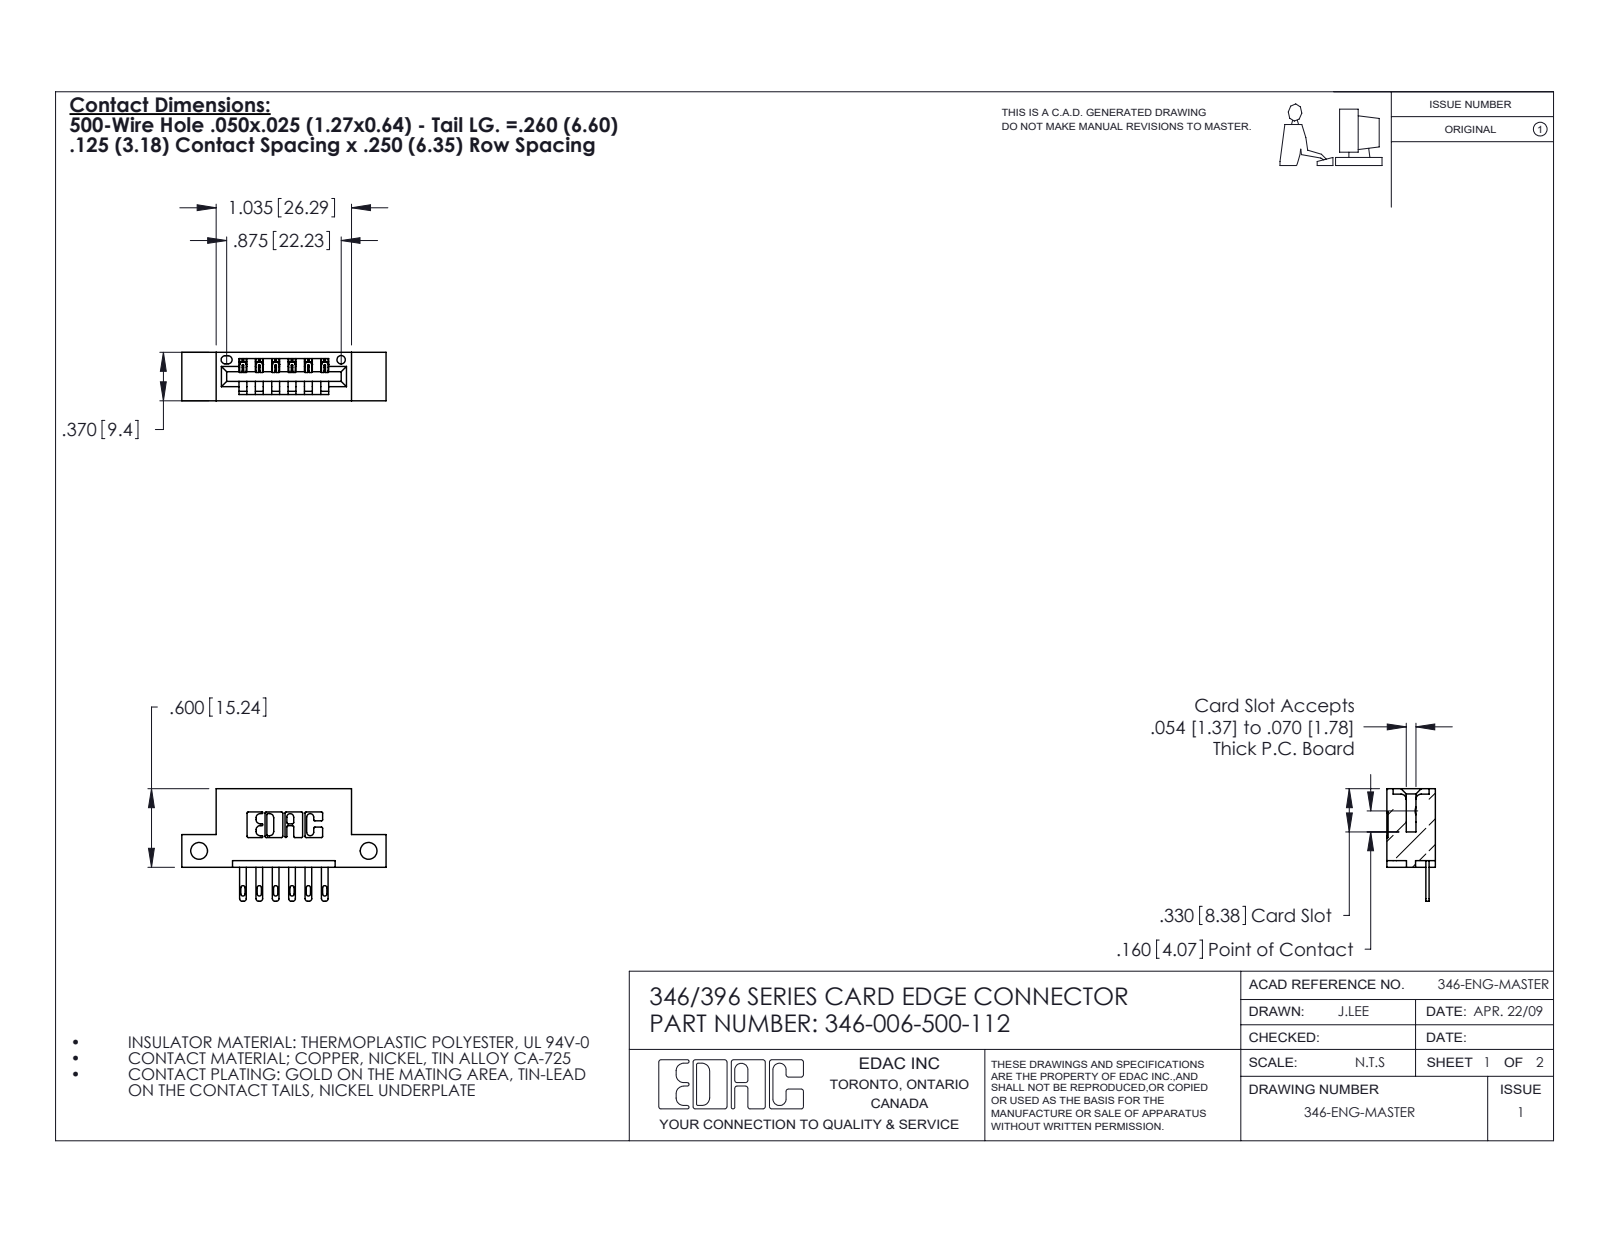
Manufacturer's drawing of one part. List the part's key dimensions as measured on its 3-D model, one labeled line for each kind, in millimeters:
Part name (STEP PRODUCT): 345-292-001_345-293-100; 346 Part_Flush Mounting Lugs - Side Mount; 346-006-500-112
STEP written by: SolidWorks 2020 (CONFIG_CONTROL_DESIGN)
Units: millimetres
Bodies: 7 solids, 446 faces (280 planar, 166 cylindrical, 0 other)
Overall size (bounding box): 39.6 × 21.8 × 9.4
Volume: 3 460 mm³ · Surface area: 3 806 mm²
Round holes (diameter × count): ⌀3.3 ×2, ⌀1.6 ×1
Partial cylindrical surfaces — rounded edges, fillets, slot ends (radius × count): R0.3 ×22, R0.2 ×12, R0.4 ×12, R0.5 ×12, R0.2 ×6, R0.8 ×6, R0.7 ×3, R0.8 ×2
Main face-to-face distances: 6.4, 9.4, 1.2, 8.2, 1.8, 7.6, 0.6, 3.8, 5.6, 2.5
Hole centre spacings: 32.9
